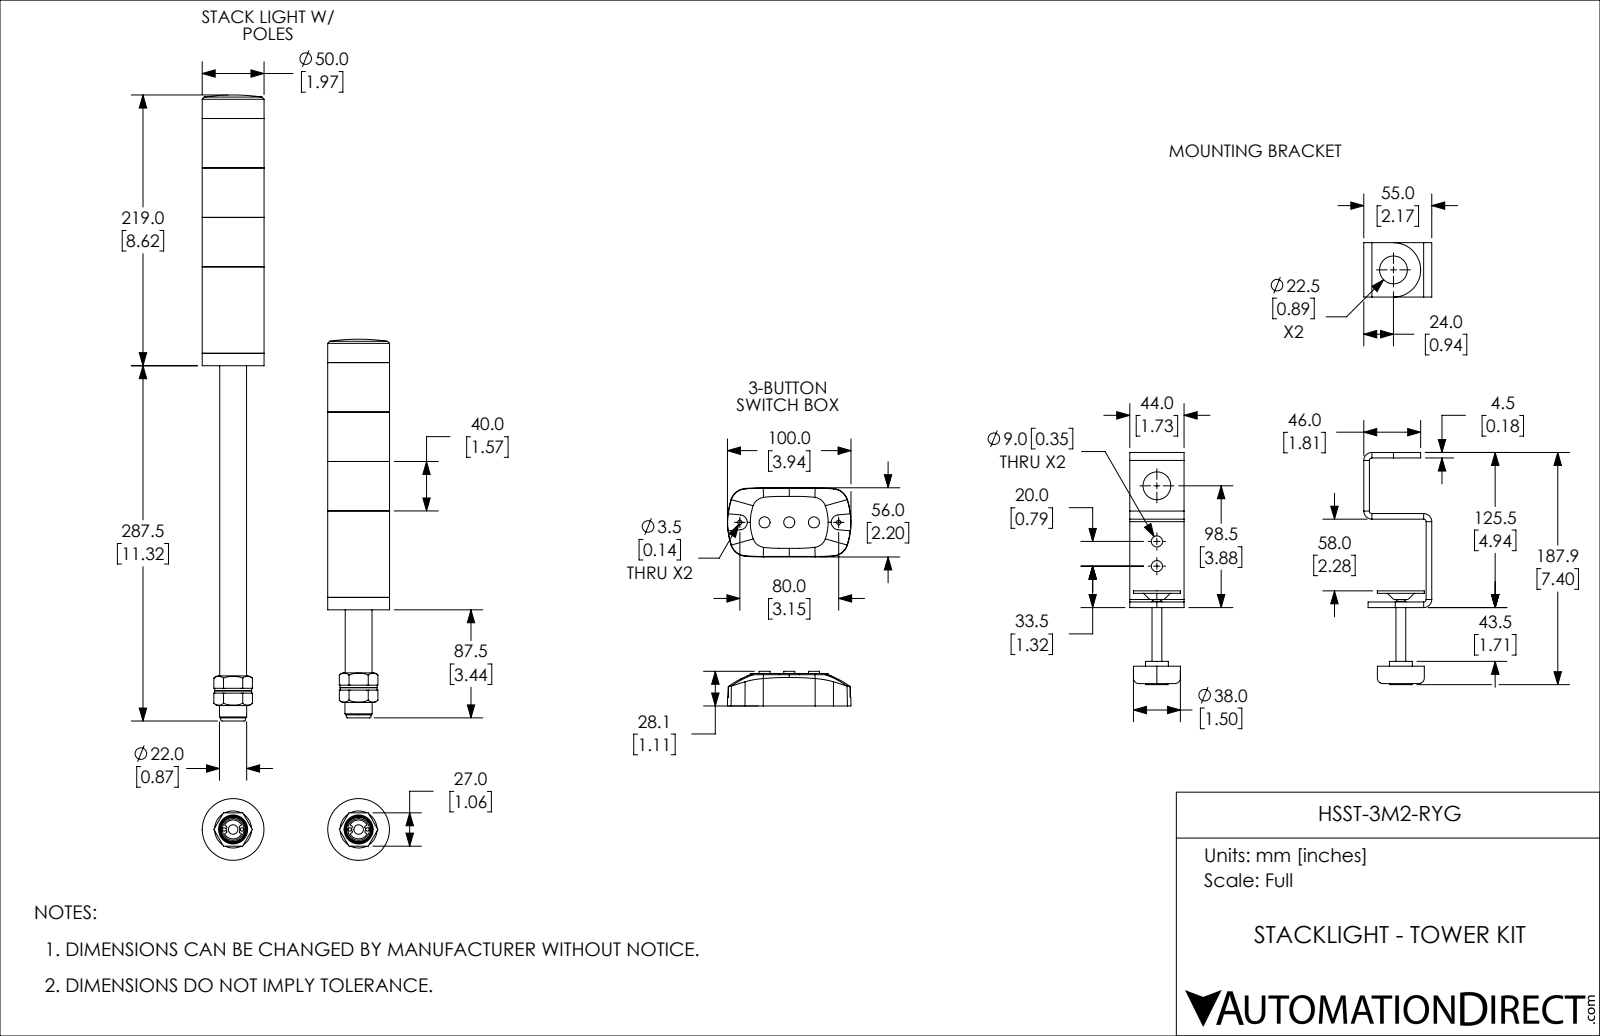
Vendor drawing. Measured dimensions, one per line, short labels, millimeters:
name: HSST-3M2-RYG_SHORT-POLE; HSST-3M2-RYG_BRACKET; HSST-3M2-RYG_SWITCH; HSST-3M2-RYG_LONG-POLE (+1 more)
written by: SolidWorks 2018 (AUTOMOTIVE_DESIGN)
unit: mm
bodies: 26 solids, 413 faces (141 planar, 202 cylindrical, 70 other)
size: 506.5 × 379.8 × 56
volume: 1 102 000 mm³; area: 265 700 mm²
holes: 4× ⌀3.2, 2× ⌀3.5, 2× ⌀7.7, 2× ⌀9, 2× ⌀17.7, 2× ⌀22, 2× ⌀22.5, 2× ⌀38.2, 2× ⌀41.8, 2× ⌀45.2, 2× ⌀47.1, 2× ⌀47.1
bosses: 3× ⌀8.9, 2× ⌀50, 2× ⌀30, 2× ⌀21.7, 1× ⌀38, 1× ⌀18.5, 1× ⌀18, 1× ⌀5
rounds: 4× R0.5, 4× R1.5, 2× R1, 2× R6, 2× R22, 1× R5.1
face distances: 40, 197.5, 80, 237.5, 157.5, 120, 117.5, 277.5, 297.8, 217.8
hole spacings: 7.2, 101.6, 94.4, 108.8, 14.4, 6, 20, 45
